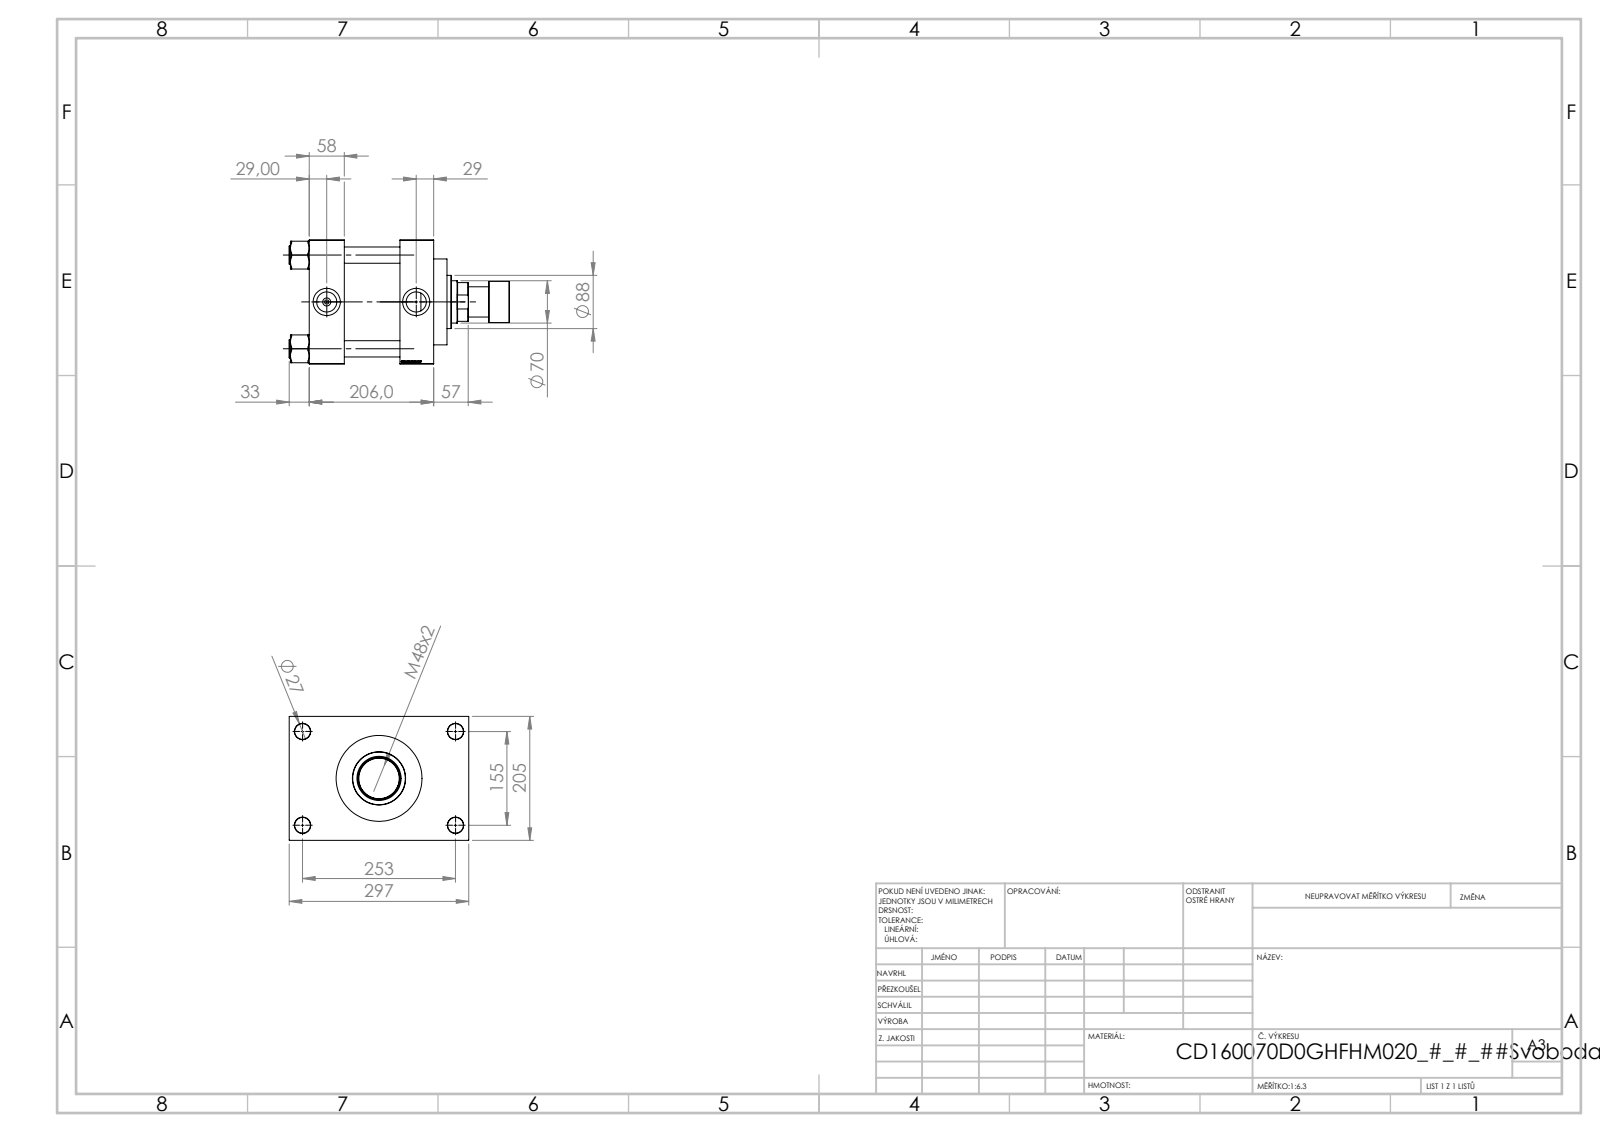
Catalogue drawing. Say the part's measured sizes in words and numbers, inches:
The part is named "V215CR_ROD_END_F; V215CD_NUT_M5_D; V215CD_D_Body; V215CD_D_TYCINKA (+2 more)". Its 3-D file was written by "SolidWorks 2019 (CONFIG_CONTROL_DESIGN)". It is 12 solids with 1162 faces: 548 planar, 92 cylindrical and 522 other. Overall it measures 14.331 by 11.693 by 8.071 inches. Its volume is 491 cubic inches and its surface area 1 162 square inches. Round holes: 4 of diameter 1.024, 4 of diameter 1.063, 2 of diameter 0.276, 2 of diameter 1.309, 2 of diameter 1.772, 1 of diameter 1.831, 1 of diameter 2.756, 1 of diameter 2.874, 1 of diameter 4.724, 1 of diameter 5.591, 1 of diameter 6.299. Round bosses or shafts: 4 of diameter 1.181, 1 of diameter 6.535, 1 of diameter 3.465, 1 of diameter 2.677, 1 of diameter 1.969, 1 of diameter 1.929. The main face-to-face distances are 2.283, 5.906, 3.622, 8.11, 5.827, 2.205, 8.071, 1.811, 9.882, 2.835. The hole center spacings are 1.931, 4.312, 5.841, 6.098, 6.399, 8.03, 10.084, 6.102.
